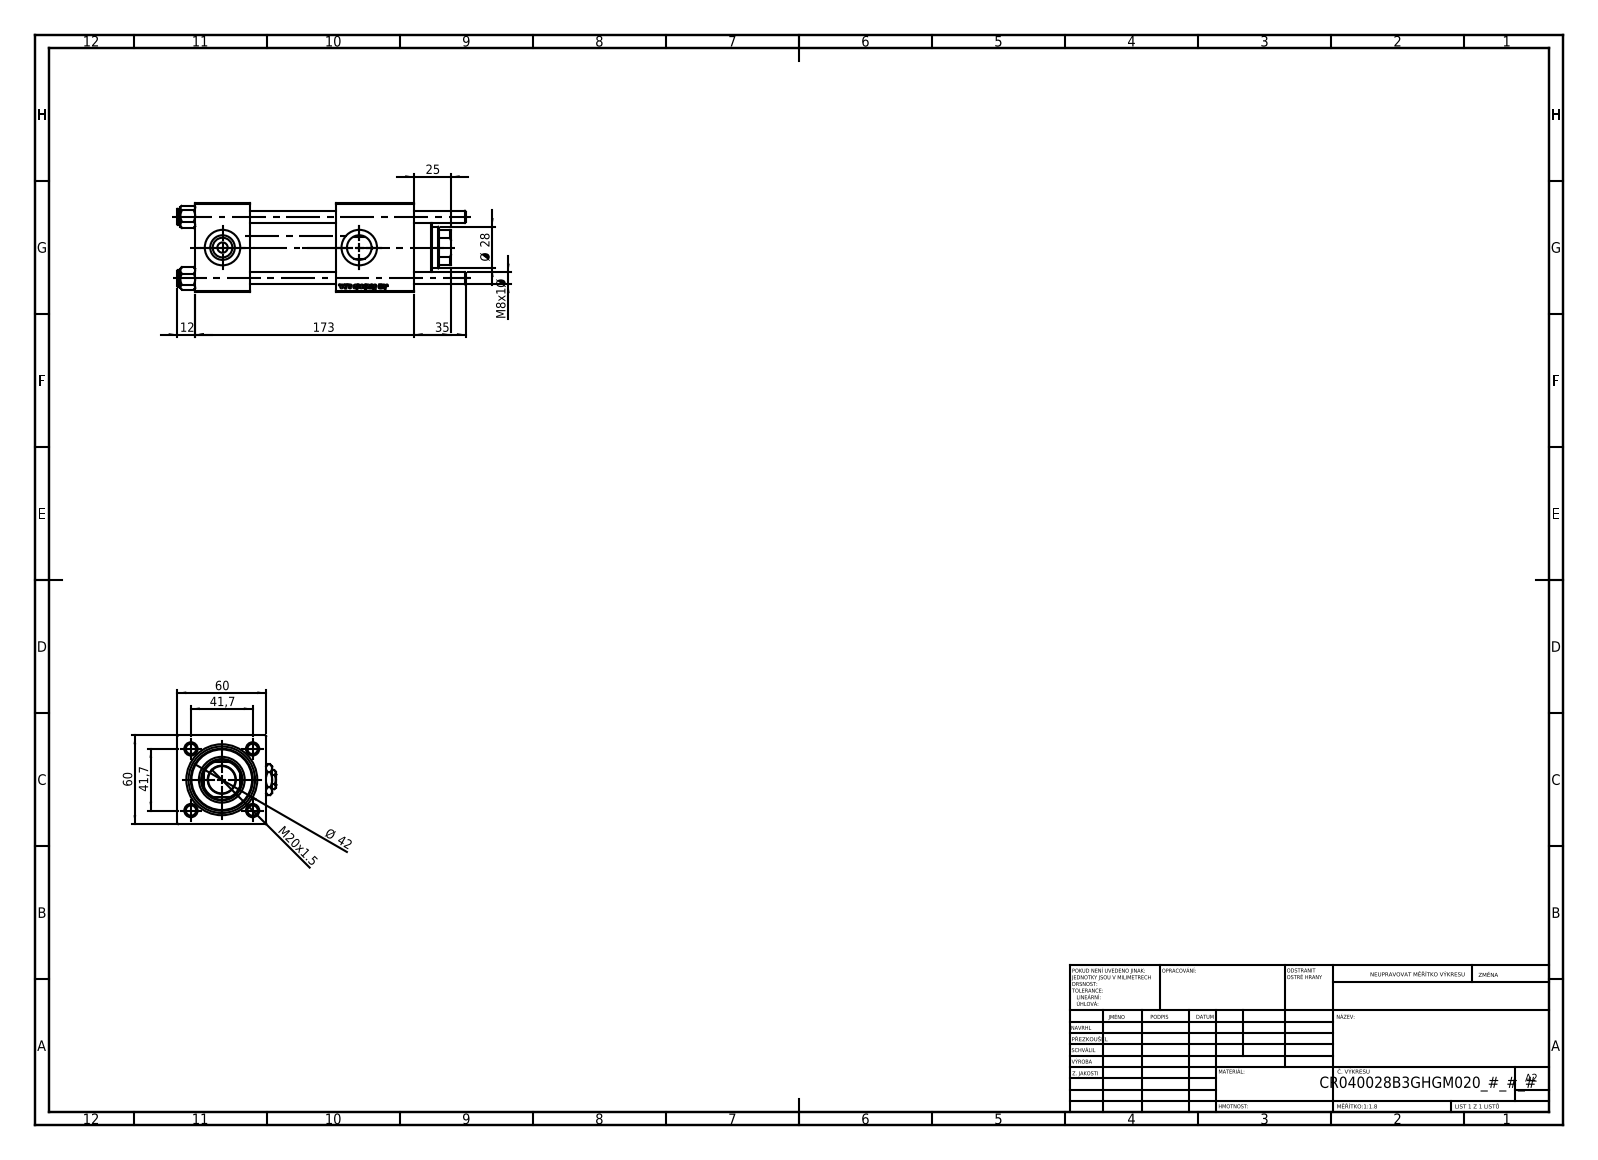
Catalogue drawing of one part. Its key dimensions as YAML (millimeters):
part_name: "V215CR_VCP_B; Zatka_pro_OIL_PORT; NUT_M5_B; V215CR_B_TYCINKA (+2 more)"
step_written_by: "SolidWorks 2019 (CONFIG_CONTROL_DESIGN)"
units: millimeters
bodies: {solids: 13, faces: 1259, planar: 481, cylindrical: 88, other: 690}
overall_size: [195, 67, 60]
volume: 432328
surface_area: 122775
round_holes:
  - {diameter: 8, count: 4}
  - {diameter: 7, count: 2}
  - {diameter: 16.66, count: 2}
  - {diameter: 24, count: 2}
  - {diameter: 18.5, count: 1}
  - {diameter: 28, count: 1}
  - {diameter: 31, count: 1}
  - {diameter: 40, count: 1}
  - {diameter: 45, count: 1}
round_bosses_or_shafts:
  - {diameter: 11, count: 4}
  - {diameter: 46, count: 1}
  - {diameter: 42, count: 1}
partial_cylinders:
  - {radius: 13.5, count: 1}
face_to_face_distances: [60, 37, 58, 95, 53, 119.3, 82.3, 24.3, 148, 111]
hole_center_spacings: [29.49, 41.7, 58.97, 92.5]
